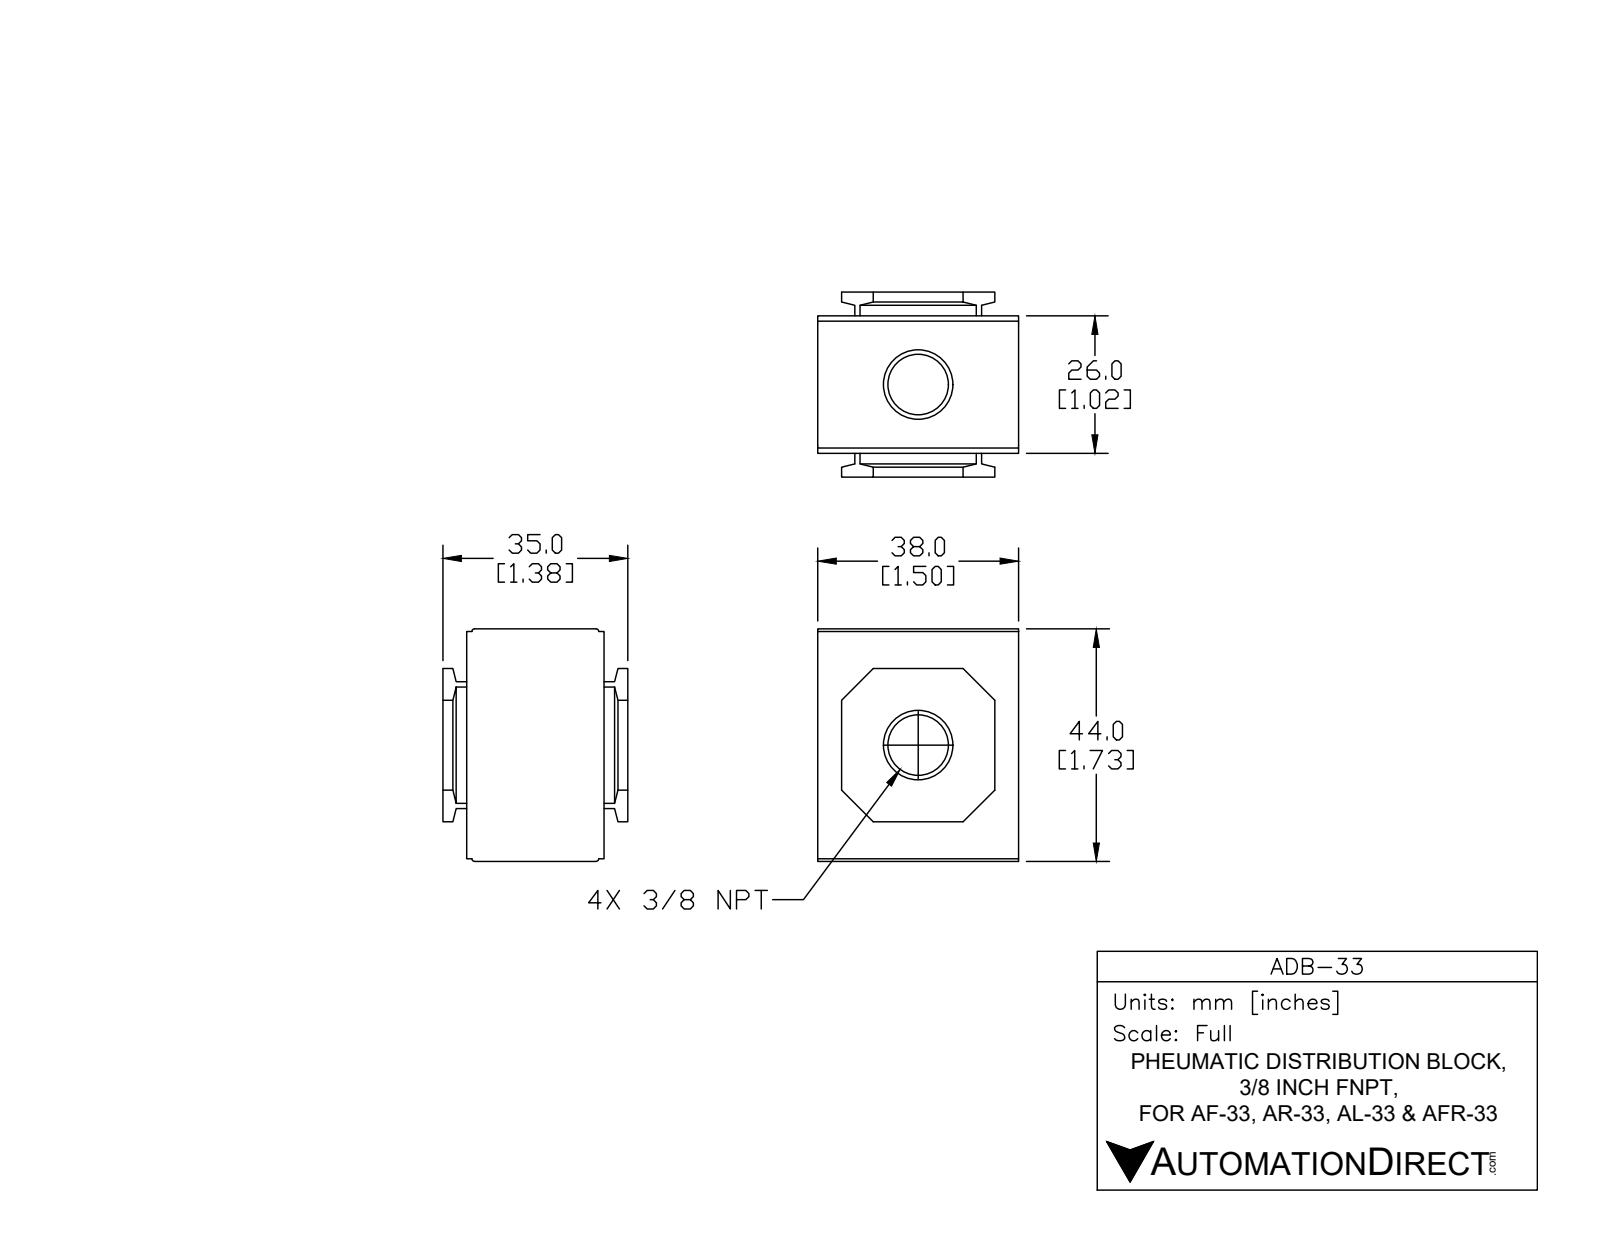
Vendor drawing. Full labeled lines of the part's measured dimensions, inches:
Part name (STEP PRODUCT): ADB-33
STEP written by: SolidWorks 2014 (AUTOMOTIVE_DESIGN)
Units: inches
Bodies: 1 solid, 64 faces (44 planar, 12 cylindrical, 8 other)
Overall size (bounding box): 1.732 × 1.496 × 1.378
Volume: 2.301 in³ · Surface area: 17.31 in²
Round holes (diameter × count): ⌀0.589 ×2
Partial cylindrical surfaces — rounded edges, fillets, slot ends (radius × count): R0.02 ×4
Main face-to-face distances: 0.177, 1.496, 1.201, 1.024, 1.732, 1.378, 0.276, 1.319, 0.098, 1.043
